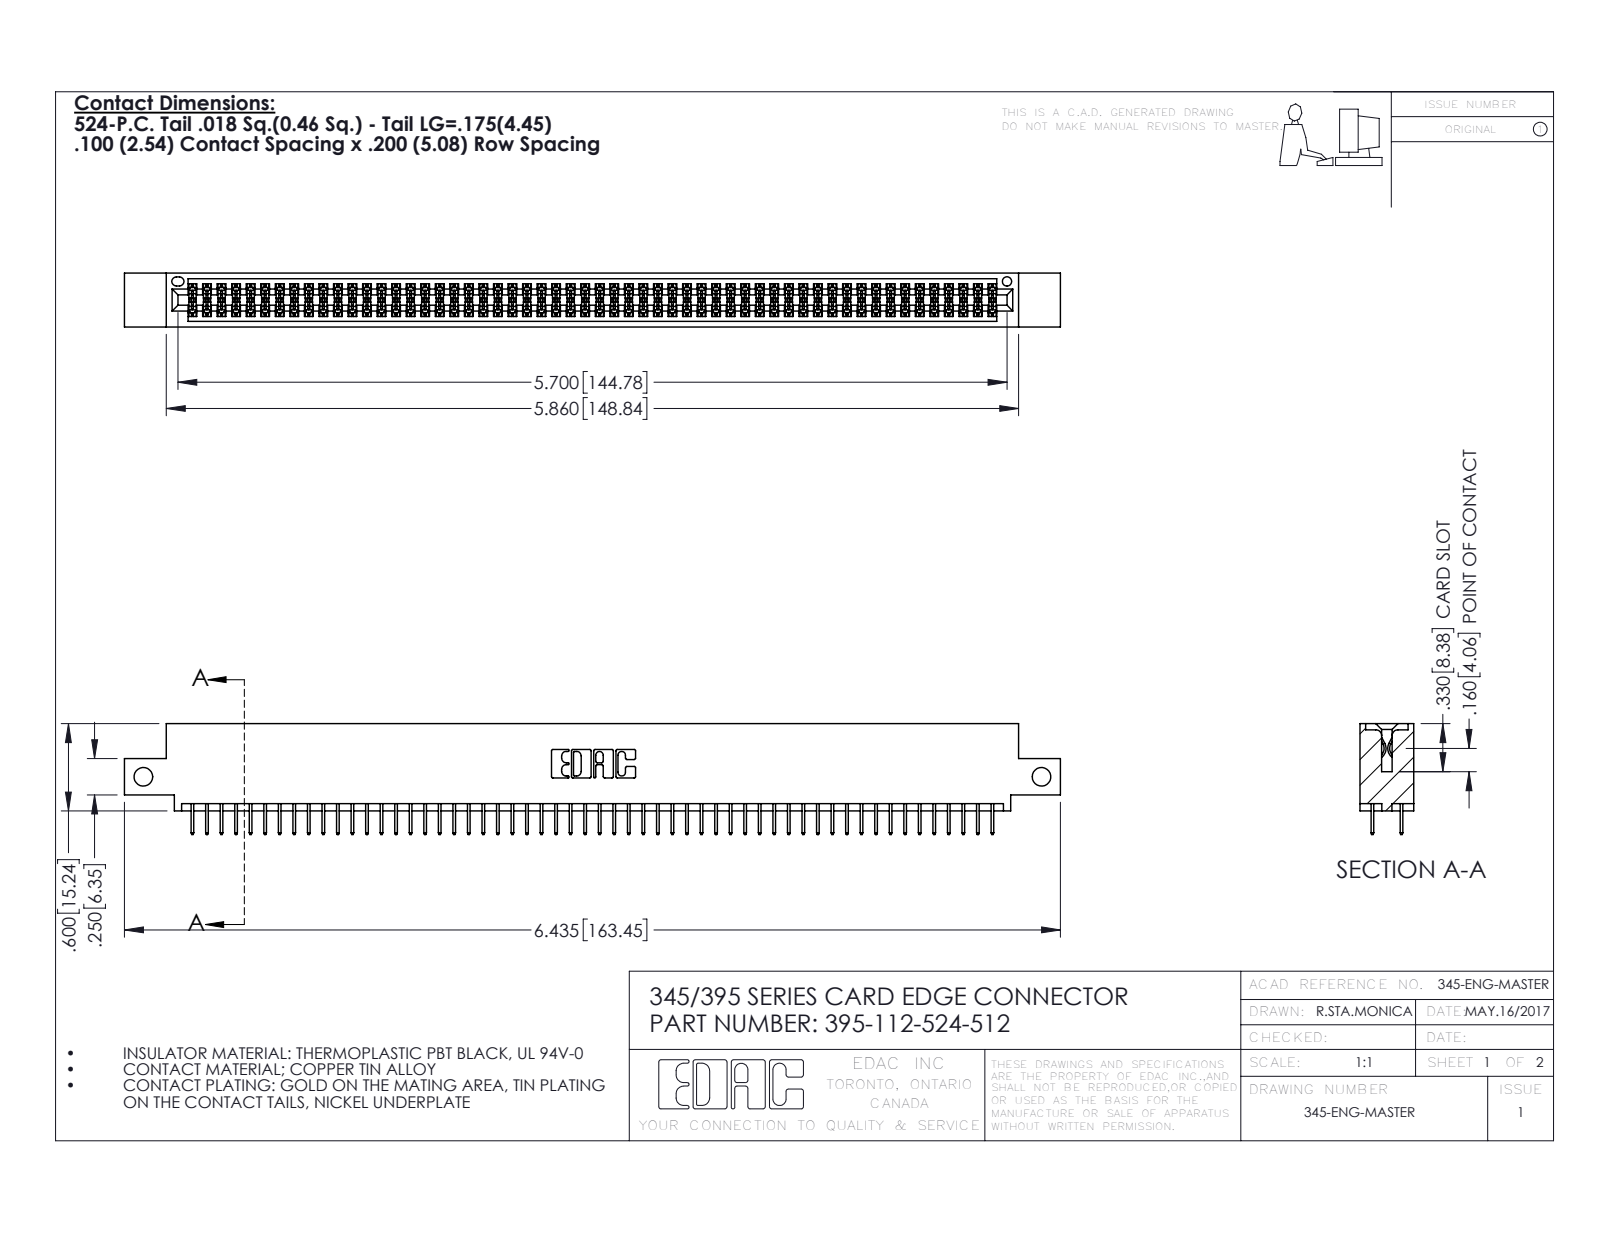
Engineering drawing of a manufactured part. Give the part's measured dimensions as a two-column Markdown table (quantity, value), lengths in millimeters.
| quantity | value |
| --- | --- |
| part name | 395-112-524-512; 345 Part_0.110 Offset - Side Mount; 345-292-001_345-293-124 |
| STEP written by | SolidWorks 2016 (CONFIG_CONTROL_DESIGN) |
| units | millimeters |
| bodies | 113 solids, 6178 faces (4452 planar, 1726 cylindrical, 0 other) |
| overall size | 163.4 × 19.4 × 9.4 |
| volume | 15 700 mm³ |
| surface area | 22 950 mm² |
| round holes (diameter × count) | 3.3 × 2, 1.6 × 1 |
| partial cylindrical surfaces (radius × count) | 0.2 × 168, 0.3 × 22, 0.2 × 6, 0.8 × 6, 0.7 × 3, 0.4 × 2, 0.5 × 2, 0.6 × 2 |
| main face-to-face distances | 1.8, 7.6, 5.1, 9.4, 2.5, 6.9, 0.6, 5.7, 1.8, 4.4 |
| hole center spacings | 156.8 |
